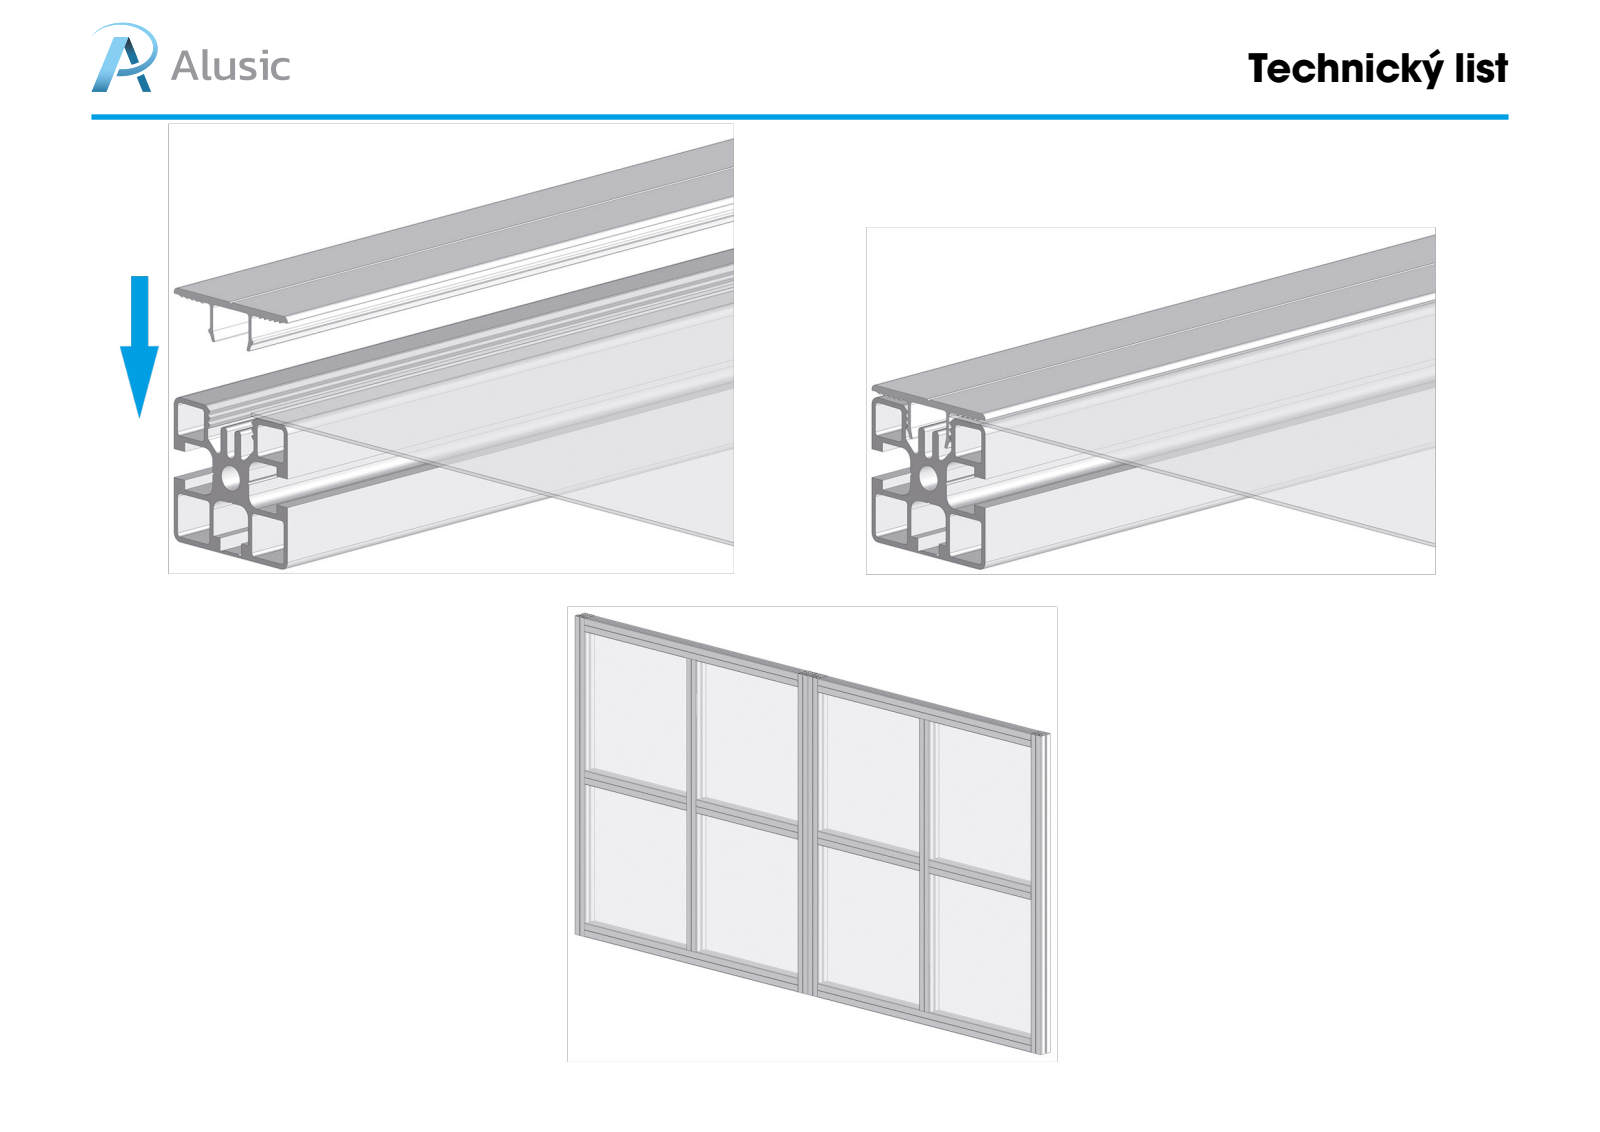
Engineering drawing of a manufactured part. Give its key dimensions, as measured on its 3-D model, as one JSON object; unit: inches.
{"part_name": "084.101.062", "step_written_by": "SolidWorks 2018 (AUTOMOTIVE_DESIGN)", "units": "inches", "bodies": {"solids": 1, "faces": 110, "planar": 53, "cylindrical": 57, "other": 0}, "overall_size": [3.937, 1.772, 0.506], "volume_in3": 0.713, "surface_area_in2": 22.1, "partial_cylinders_radius": [[0.004, 23], [0.01, 4], [0.039, 4], [0.008, 2], [0.02, 2], [0.059, 2]], "face_to_face_distances": [0.079, 0.039, 0.598, 0.024, 0.559, 0.074, 0.049, 0.638, 0.098, 0.049]}
